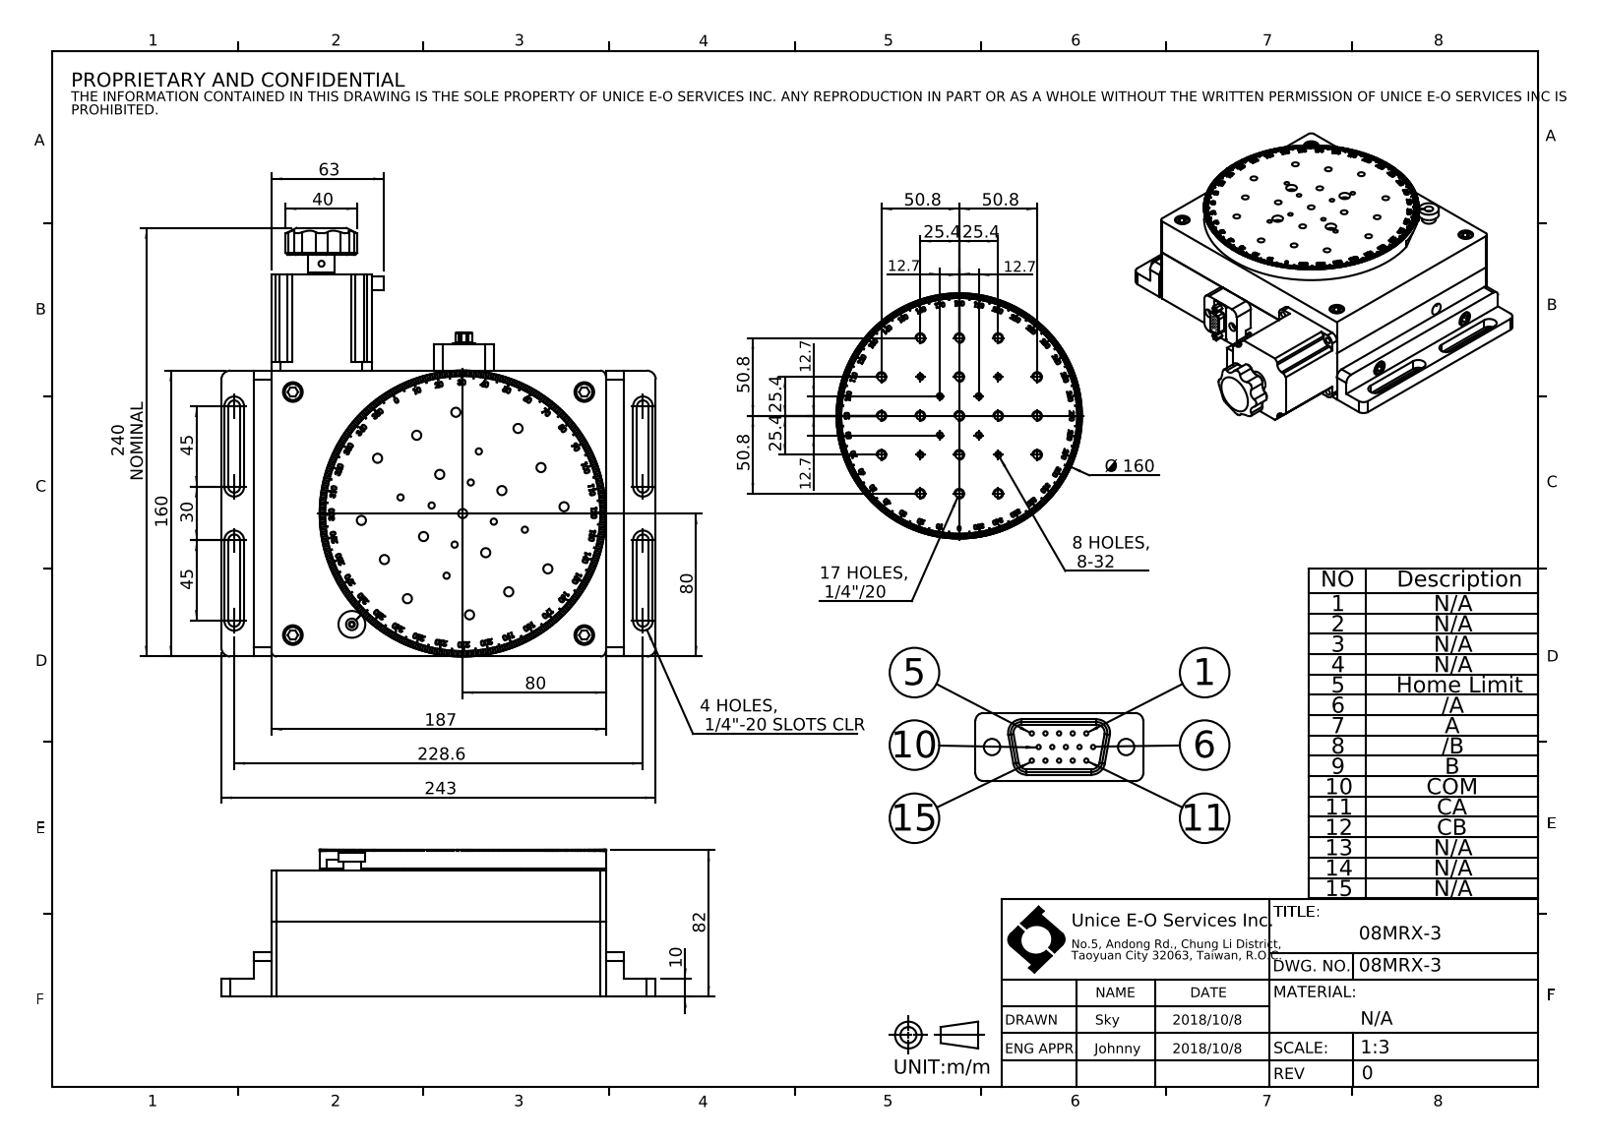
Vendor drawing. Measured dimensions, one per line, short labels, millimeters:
name: 08MRX-3
written by: SolidWorks 2016 (AUTOMOTIVE_DESIGN)
unit: mm
bodies: 0 solids, 1074 faces (740 planar, 257 cylindrical, 77 other)
size: 243 × 239.8 × 82
holes: 17× ⌀5.11, 12× ⌀4.5, 10× ⌀0.8, 8× ⌀3.45, 6× ⌀11, 4× ⌀8, 4× ⌀8.6, 3× ⌀6.5, 2× ⌀2.5, 2× ⌀3.4, 2× ⌀5, 1× ⌀1
bosses: 5× ⌀10, 2× ⌀15, 1× ⌀160, 1× ⌀84
rounds: 14× R5, 8× R3.3, 8× R4, 8× R5.5, 8× R7.41, 7× R0.5, 4× R1.5, 4× R2
face distances: 42, 10, 70.5, 28.5, 72, 82, 40, 11.5, 1.5, 30
hole spacings: 25.4, 40.16, 50.8, 56.8, 56.79, 35.92, 91.58, 53.88
